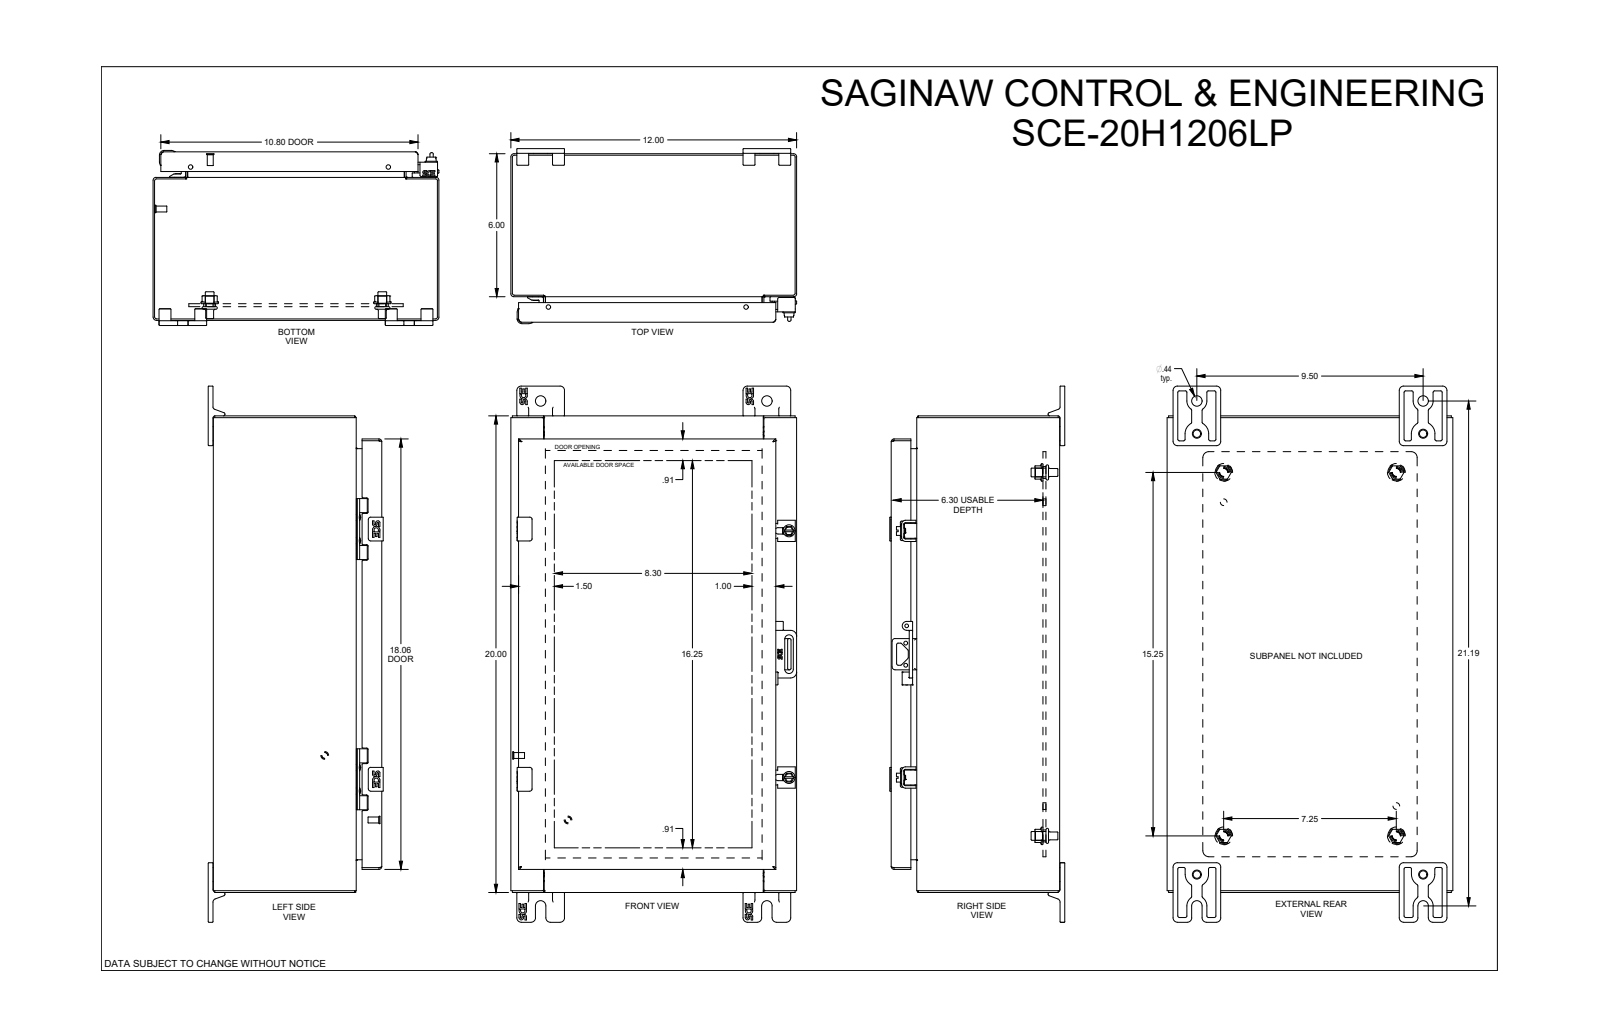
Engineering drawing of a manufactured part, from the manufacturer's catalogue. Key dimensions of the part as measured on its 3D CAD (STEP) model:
Part name (STEP PRODUCT): SCE-20H1206LP
STEP written by: SolidWorks 2021 (AUTOMOTIVE_DESIGN)
Units: inches
Bodies: 34 solids, 1808 faces (705 planar, 753 cylindrical, 350 other)
Overall size (bounding box): 22.5 × 12 × 7.343
Volume: 105.5 in³ · Surface area: 2 483 in²
Round holes (diameter × count): ⌀0.172 ×4, ⌀0.205 ×4, ⌀0.218 ×4, ⌀0.244 ×4, ⌀0.312 ×4, ⌀0.375 ×4, ⌀0.437 ×4, ⌀0.5 ×4, ⌀0.04 ×2, ⌀0.16 ×2, ⌀0.188 ×2, ⌀0.203 ×2
Round bosses / shafts (diameter × count): ⌀0.25 ×6, ⌀0.248 ×5, ⌀0.59 ×4, ⌀0.376 ×4, ⌀0.375 ×4, ⌀0.33 ×4, ⌀0.31 ×4, ⌀0.24 ×4
Partial cylindrical surfaces — rounded edges, fillets, slot ends (radius × count): R0.025 ×68, R0.01 ×62, R0.03 ×32, R0.06 ×26, R0.015 ×24, R0.185 ×21, R0.22 ×16, R0.043 ×12
Main face-to-face distances: 0.075, 0.06, 11.925, 6.993, 7.068, 7.008, 6.933, 0.125, 5.925, 0.575
Hole centre spacings: 0.5, 1.976, 8.531, 10, 16.913, 18.839, 9.5, 14.011
